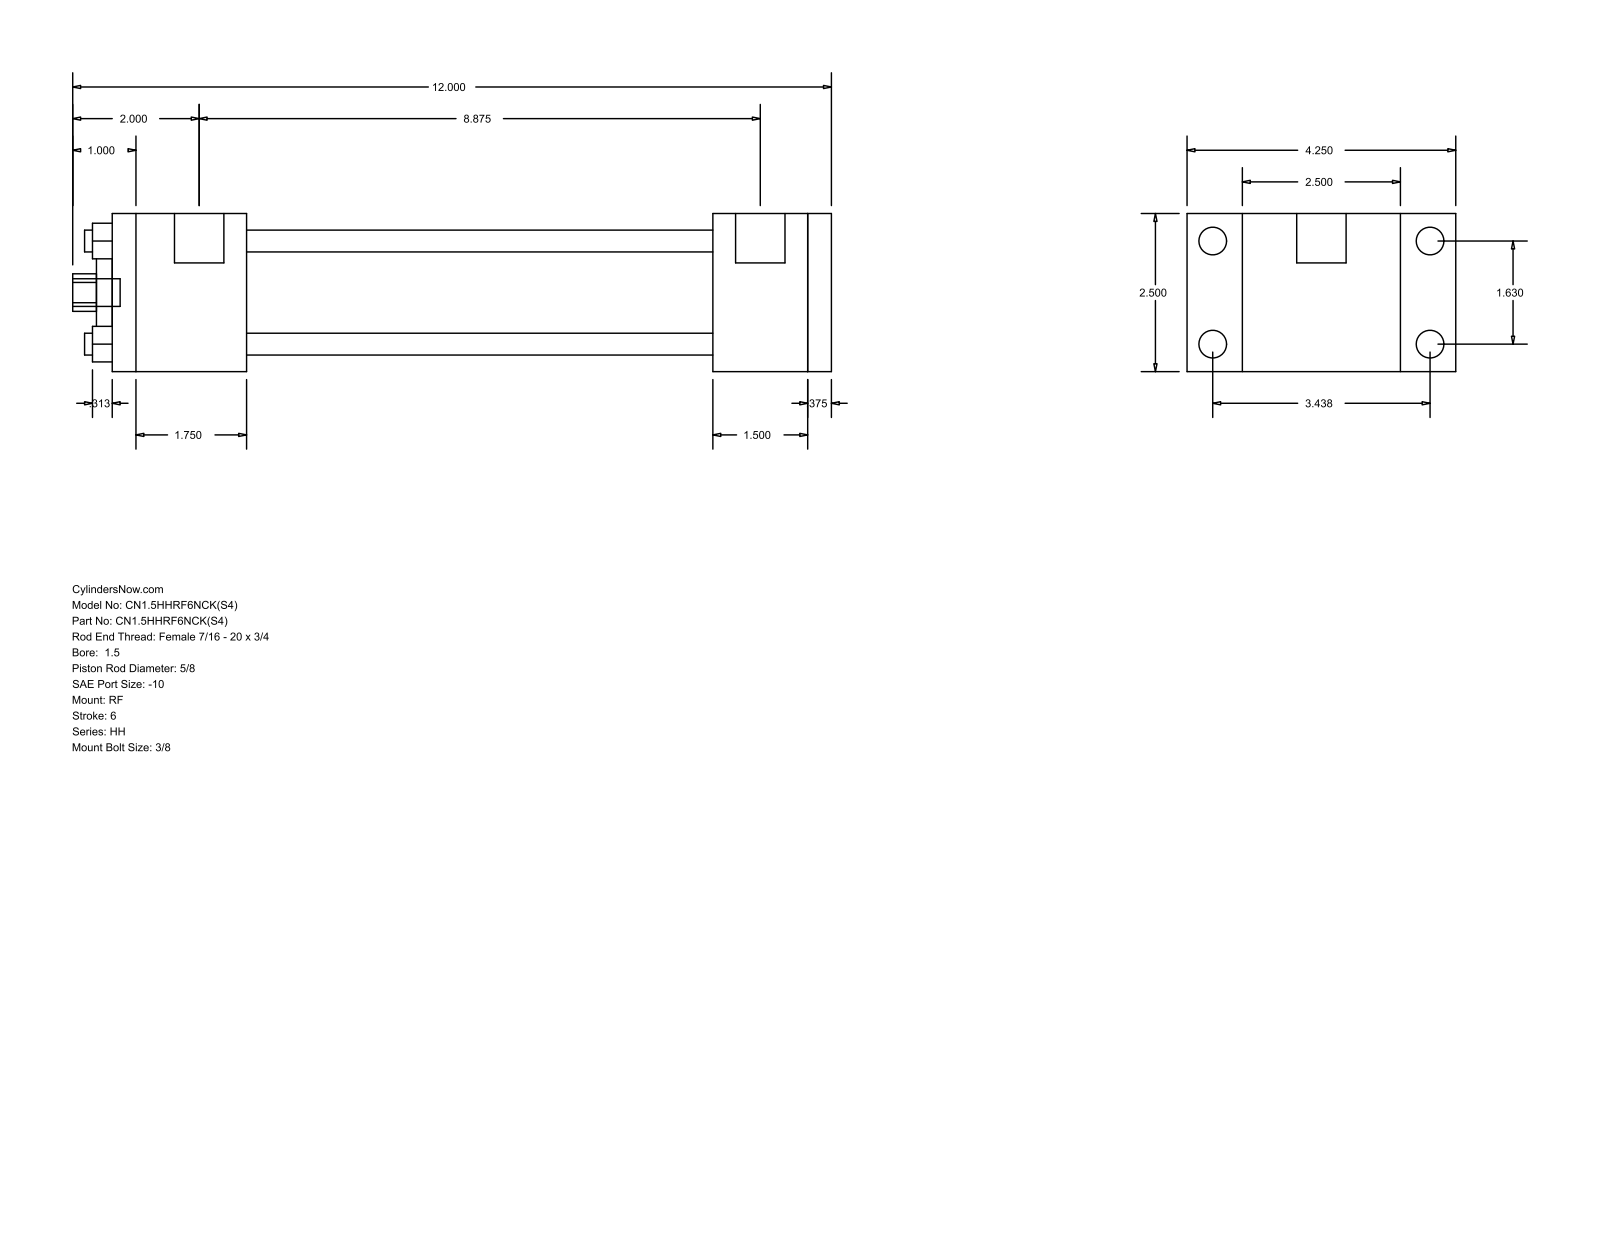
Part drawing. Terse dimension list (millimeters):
name: HH_RF__0150_0.625
written by: GSSL Pune (CONFIG_CONTROL_DESIGN)
unit: mm
bodies: 0 solids, 92 faces (64 planar, 28 cylindrical, 0 other)
size: 304.8 × 107.95 × 63.5
holes: 4× ⌀8.76, 1× ⌀15.88, 1× ⌀28.57, 1× ⌀44.45
bosses: 4× ⌀11.13, 4× ⌀5.56, 2× ⌀19.84, 1× ⌀11.11
rounds: 1× R7.54
face distances: 63.5, 288.92, 9.53, 279.39, 53.97, 241.3, 187.33, 225.42, 234.95, 38.09
hole spacings: 29.27, 41.4, 58.55
